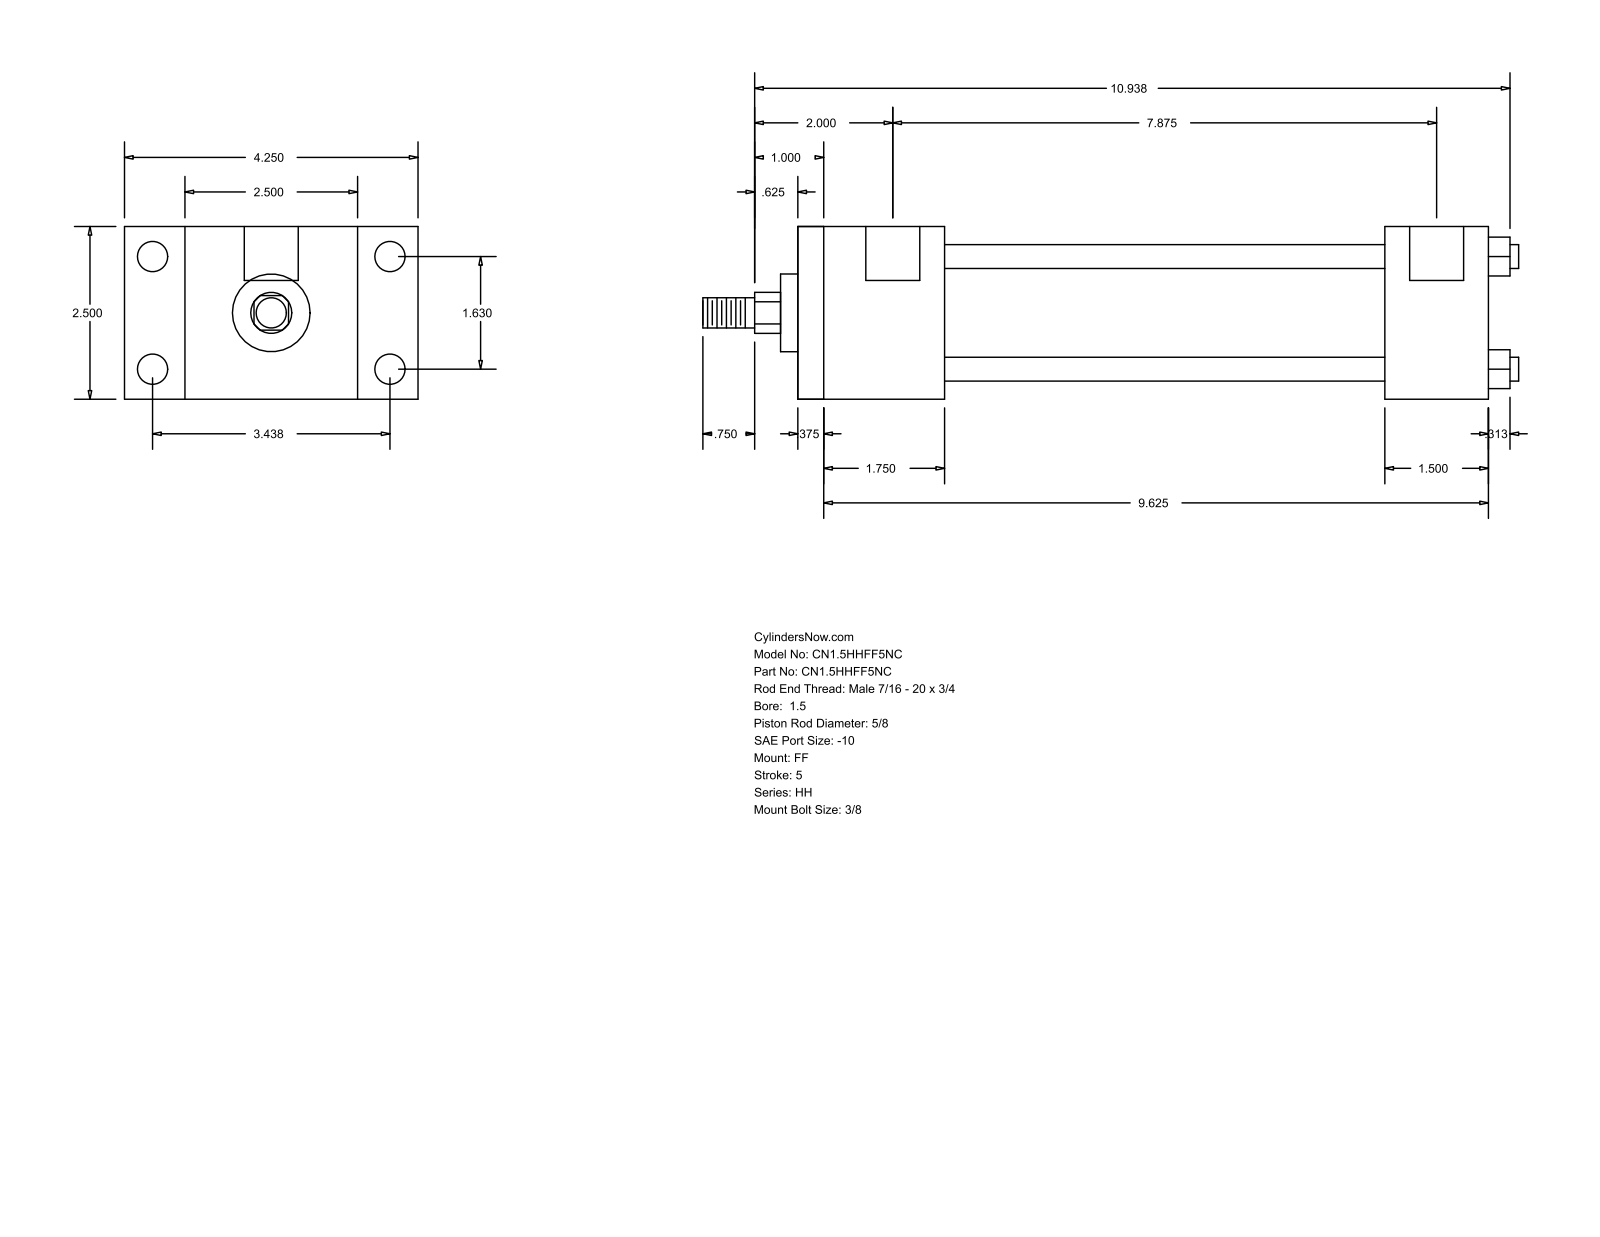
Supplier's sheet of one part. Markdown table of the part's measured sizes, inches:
| quantity | value |
| --- | --- |
| part name | HH_FF__0150_0.625 |
| STEP written by | GSSL Pune (CONFIG_CONTROL_DESIGN) |
| units | inches |
| bodies | 0 solids, 92 faces (64 planar, 28 cylindrical, 0 other) |
| overall size | 11.813 × 4.25 × 2.5 |
| round holes (diameter × count) | 0.219 × 4, 0.438 × 4, 0.781 × 2 |
| round bosses / shafts (diameter × count) | 0.345 × 4, 1.75 × 1, 1.125 × 1, 0.625 × 1, 0.437 × 1 |
| partial cylindrical surfaces (radius × count) | 0.297 × 1 |
| main face-to-face distances | 2.5, 10, 1.5, 0.375, 9.625, 1.75, 2.125, 7.875, 8.5, 8.125 |
| hole center spacings | 0.063, 1.63, 3.438, 3.805, 7.937, 8, 7.875 |
